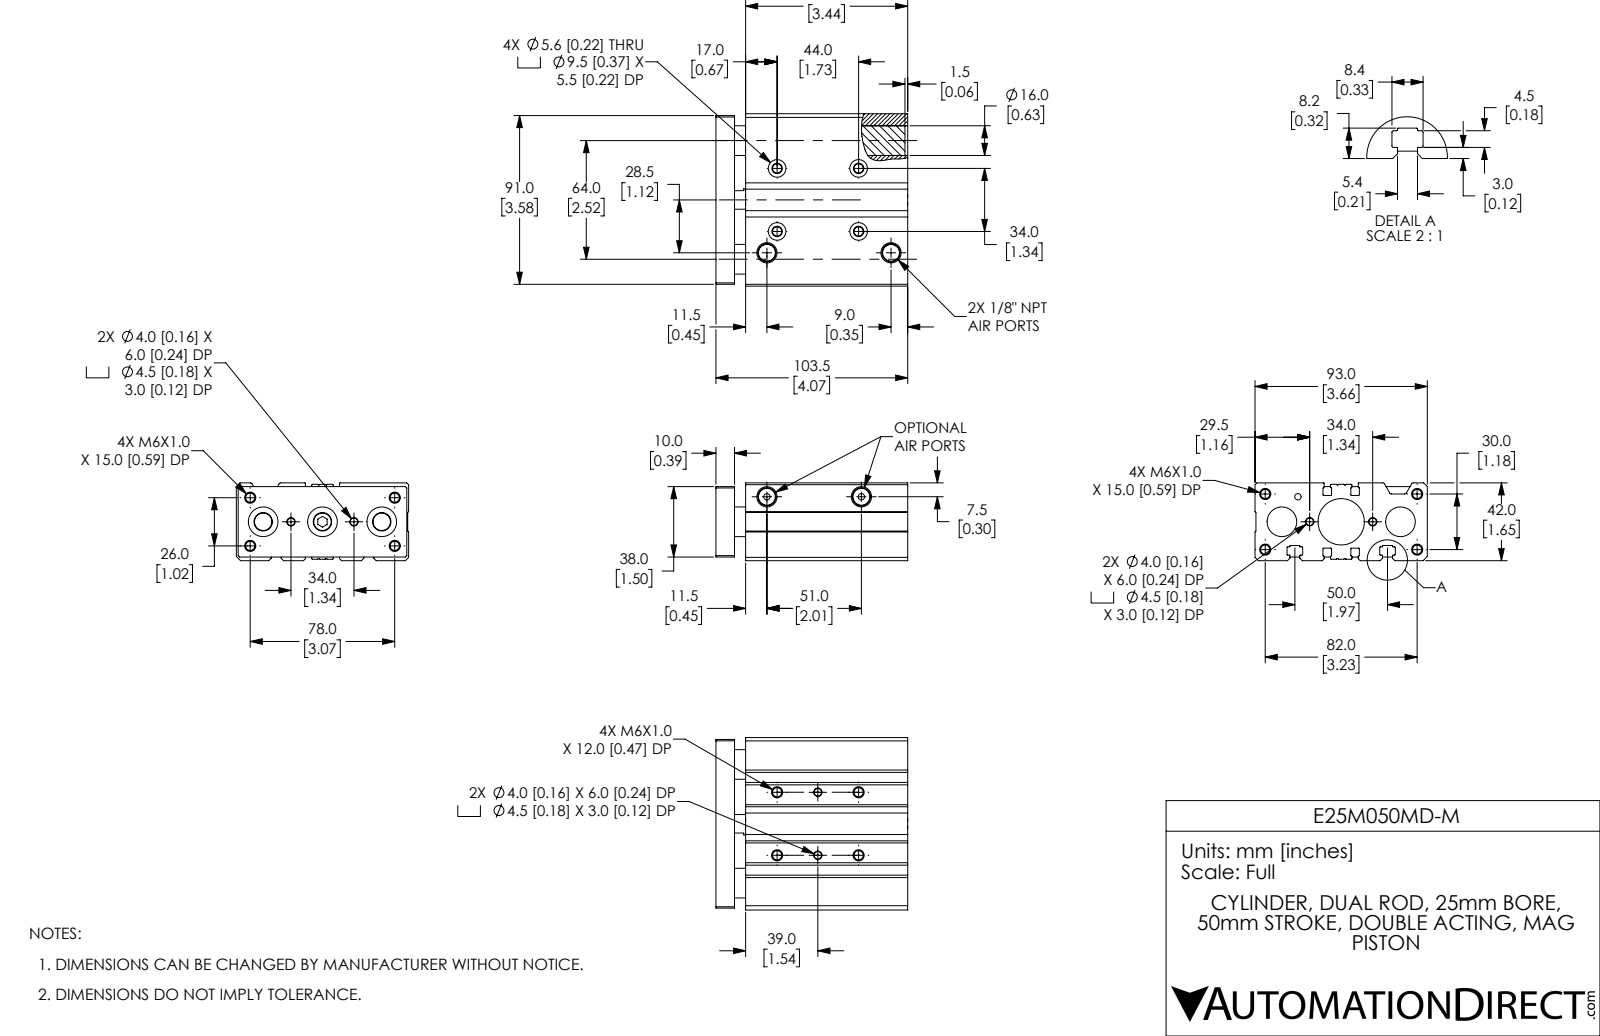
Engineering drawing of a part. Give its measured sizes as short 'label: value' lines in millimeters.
name: E25M050MD-M_BODY; E25M050MD-M; E25M050MD-M_ENDPLATE
written by: SolidWorks 2019 (CONFIG_CONTROL_DESIGN)
unit: mm
bodies: 5 solids, 423 faces (139 planar, 190 cylindrical, 94 other)
size: 103.5 × 93 × 42
volume: 317 792 mm³; area: 87 668 mm²
holes: 8× ⌀4.92, 4× ⌀4, 4× ⌀4.5, 4× ⌀4.92, 4× ⌀5.6, 4× ⌀9.5, 3× ⌀8, 3× ⌀16, 2× ⌀3.43, 2× ⌀9.91, 1× ⌀3.43, 1× ⌀16
bosses: 1× ⌀12, 1× ⌀9.91
rounds: 32× R0.2, 28× R0.4, 4× R1, 2× R0.3
face distances: 6, 42, 16, 10, 2, 103.5, 93.5, 87.5, 93, 0.8
hole spacings: 2.83, 14.76, 17.49, 22, 25.55, 28.07, 28.3, 34
